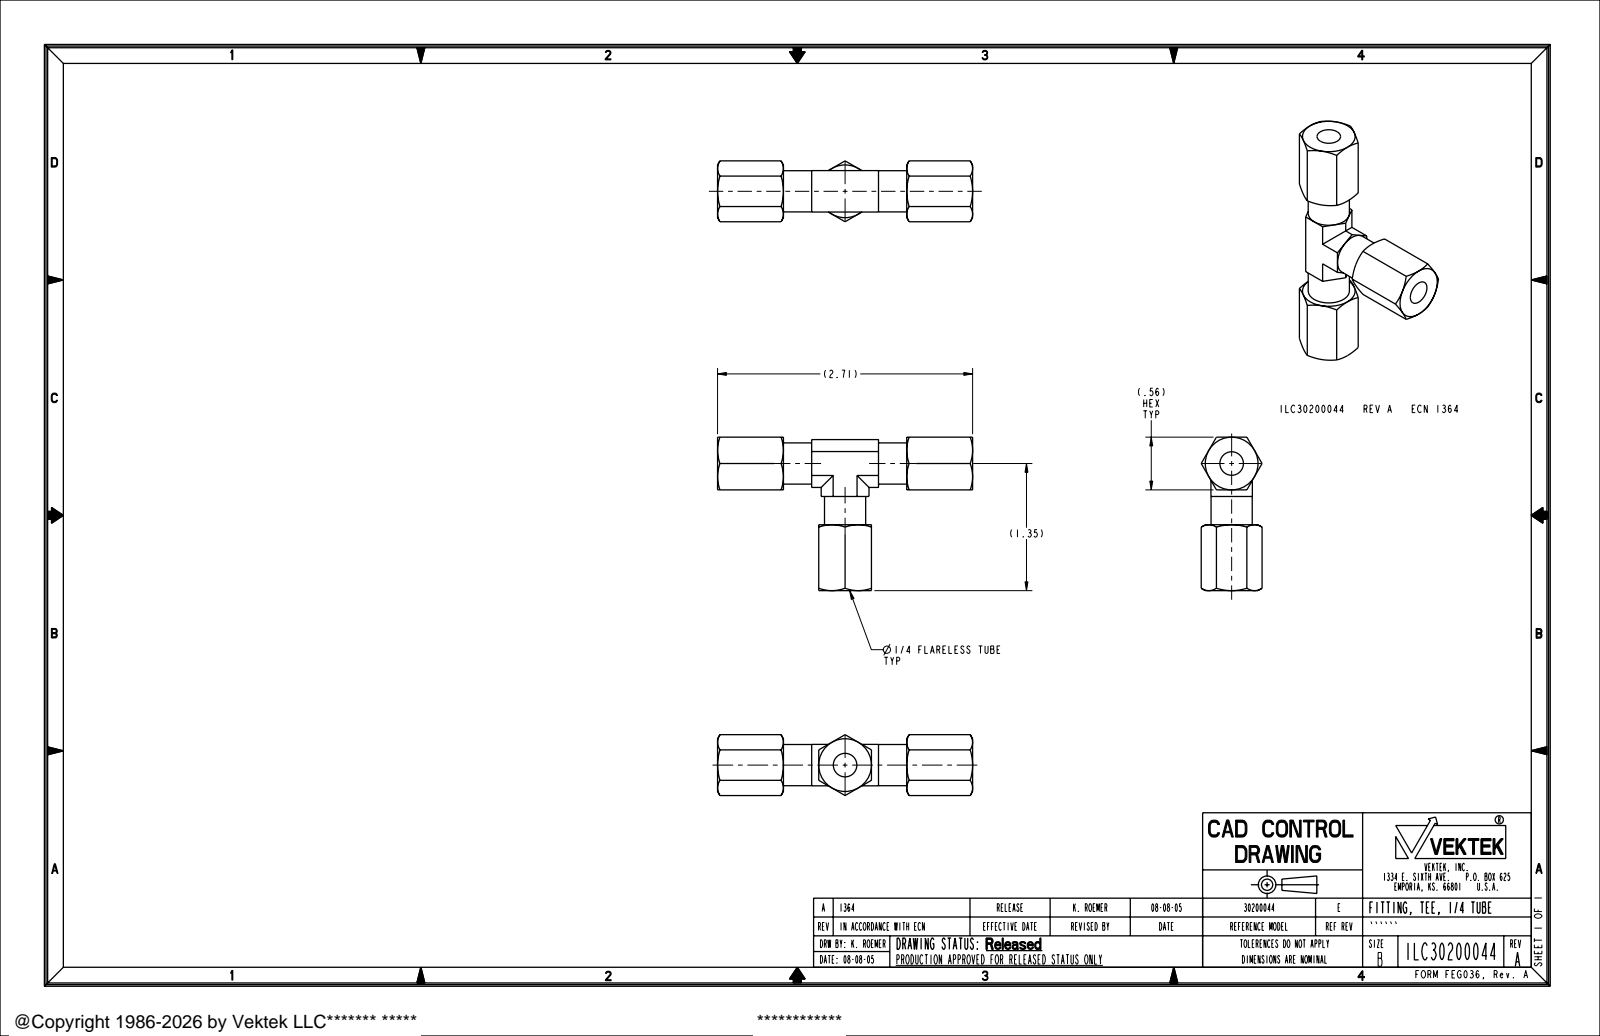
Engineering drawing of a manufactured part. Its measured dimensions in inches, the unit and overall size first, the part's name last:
Units: inches
Overall size (bounding box): 2.71 × 1.63 × 0.647
Round holes (diameter × count): ⌀0.25 ×2
Round bosses / shafts (diameter × count): ⌀0.437 ×2
Main face-to-face distances: 0.56, 0.44, 1.075, 1.635, 0.7, 1.63, 1.07, 2.71, 2.01, 0.375
Volume: 0.655 in³ · Surface area: 10.55 in²
Bodies: 1 solid, 86 faces (39 planar, 11 cylindrical, 36 other)
Part name (STEP PRODUCT): ILC30200044
STEP written by: PRO/ENGINEER BY PARAMETRIC TECHNOLOGY CORPORATION, 2004290 (AUTOMOTIVE_DESIGN_CC2)
